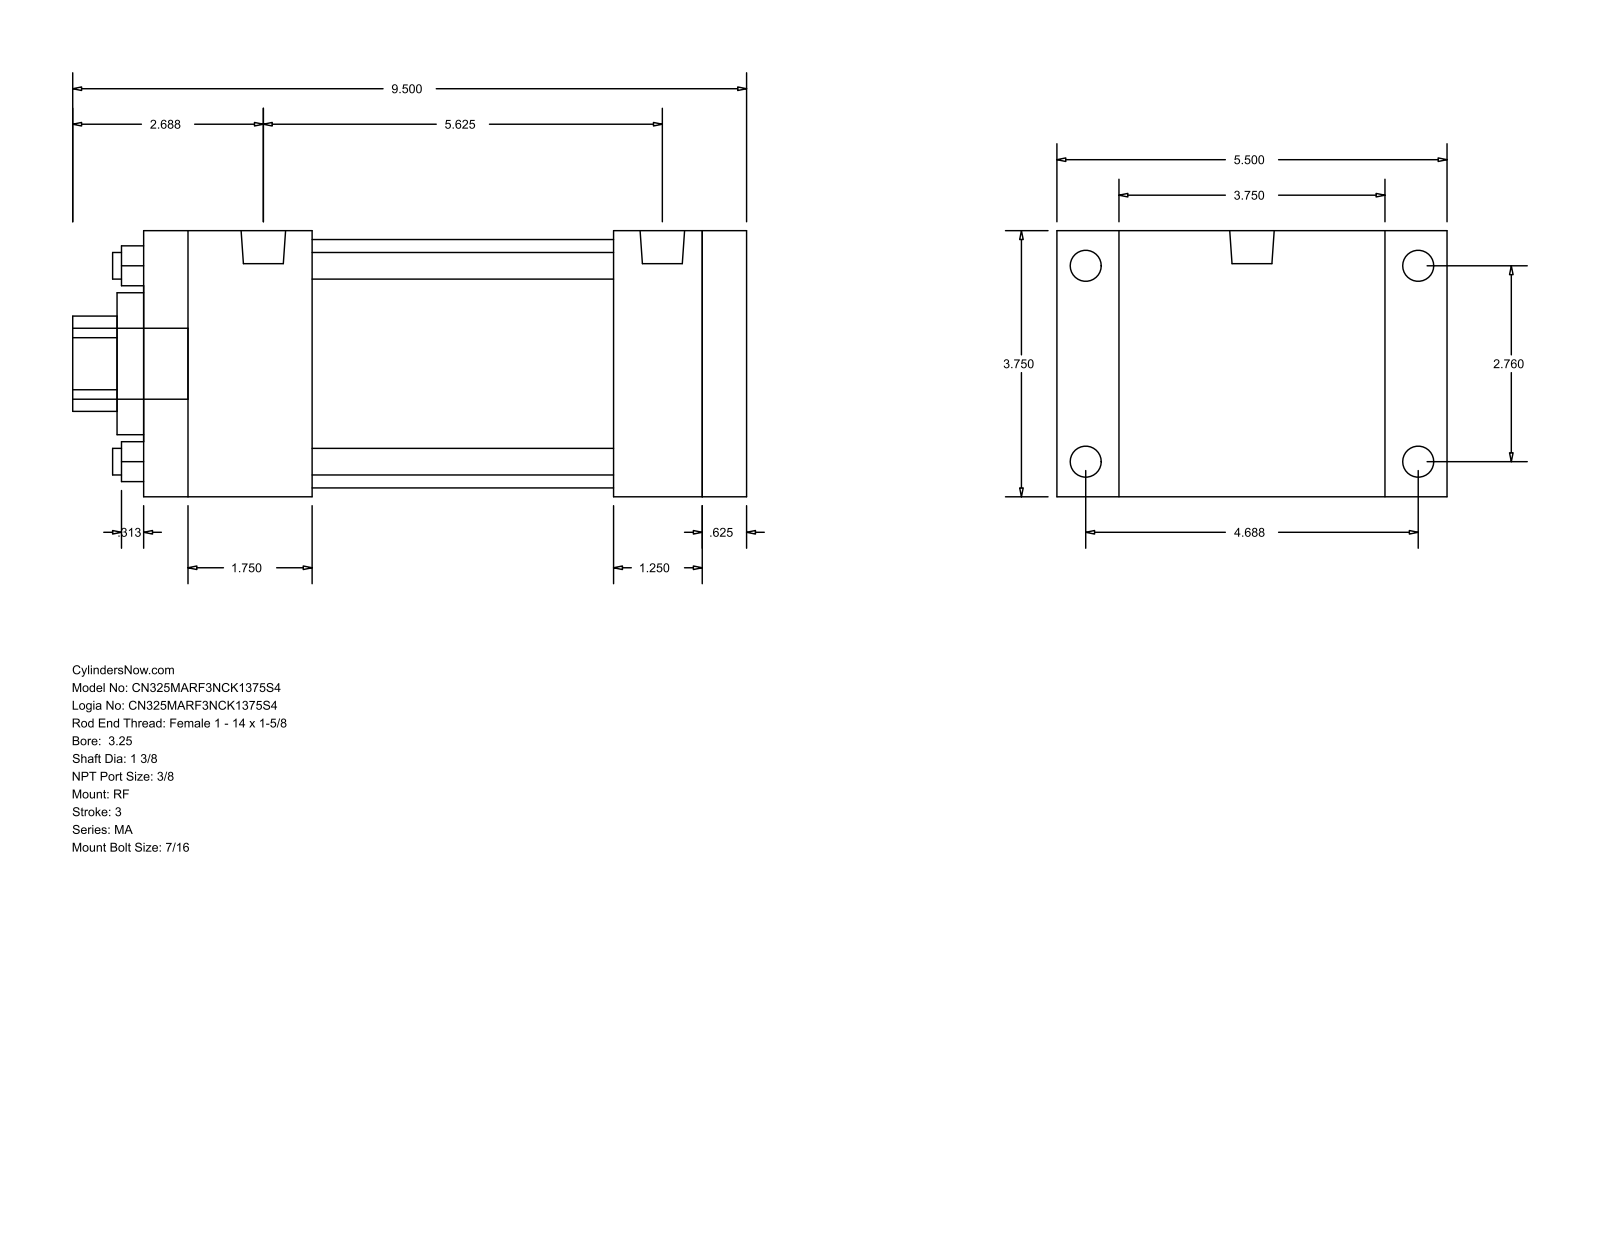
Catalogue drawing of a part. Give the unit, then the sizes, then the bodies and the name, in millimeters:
Units: millimetres
Overall size (bounding box): 241.3 × 139.7 × 95.25
Round holes (diameter × count): ⌀9.53 ×4, ⌀34.92 ×1, ⌀50.8 ×1, ⌀88.9 ×1
Round bosses / shafts (diameter × count): ⌀11.11 ×8, ⌀15.93 ×2, ⌀25.4 ×1
Partial cylindrical surfaces — rounded edges, fillets, slot ends (radius × count): R17.06 ×1
Main face-to-face distances: 95.24, 215.9, 15.87, 200.03, 22.23, 117.47, 168.28, 31.75, 47.62, 60.32
Hole centre spacings: 49.57, 70.1, 99.14
Bodies: 0 solids, 92 faces (64 planar, 28 cylindrical, 0 other)
Part name (STEP PRODUCT): MA_RF__0325_1.375
STEP written by: GSSL Pune (CONFIG_CONTROL_DESIGN)
